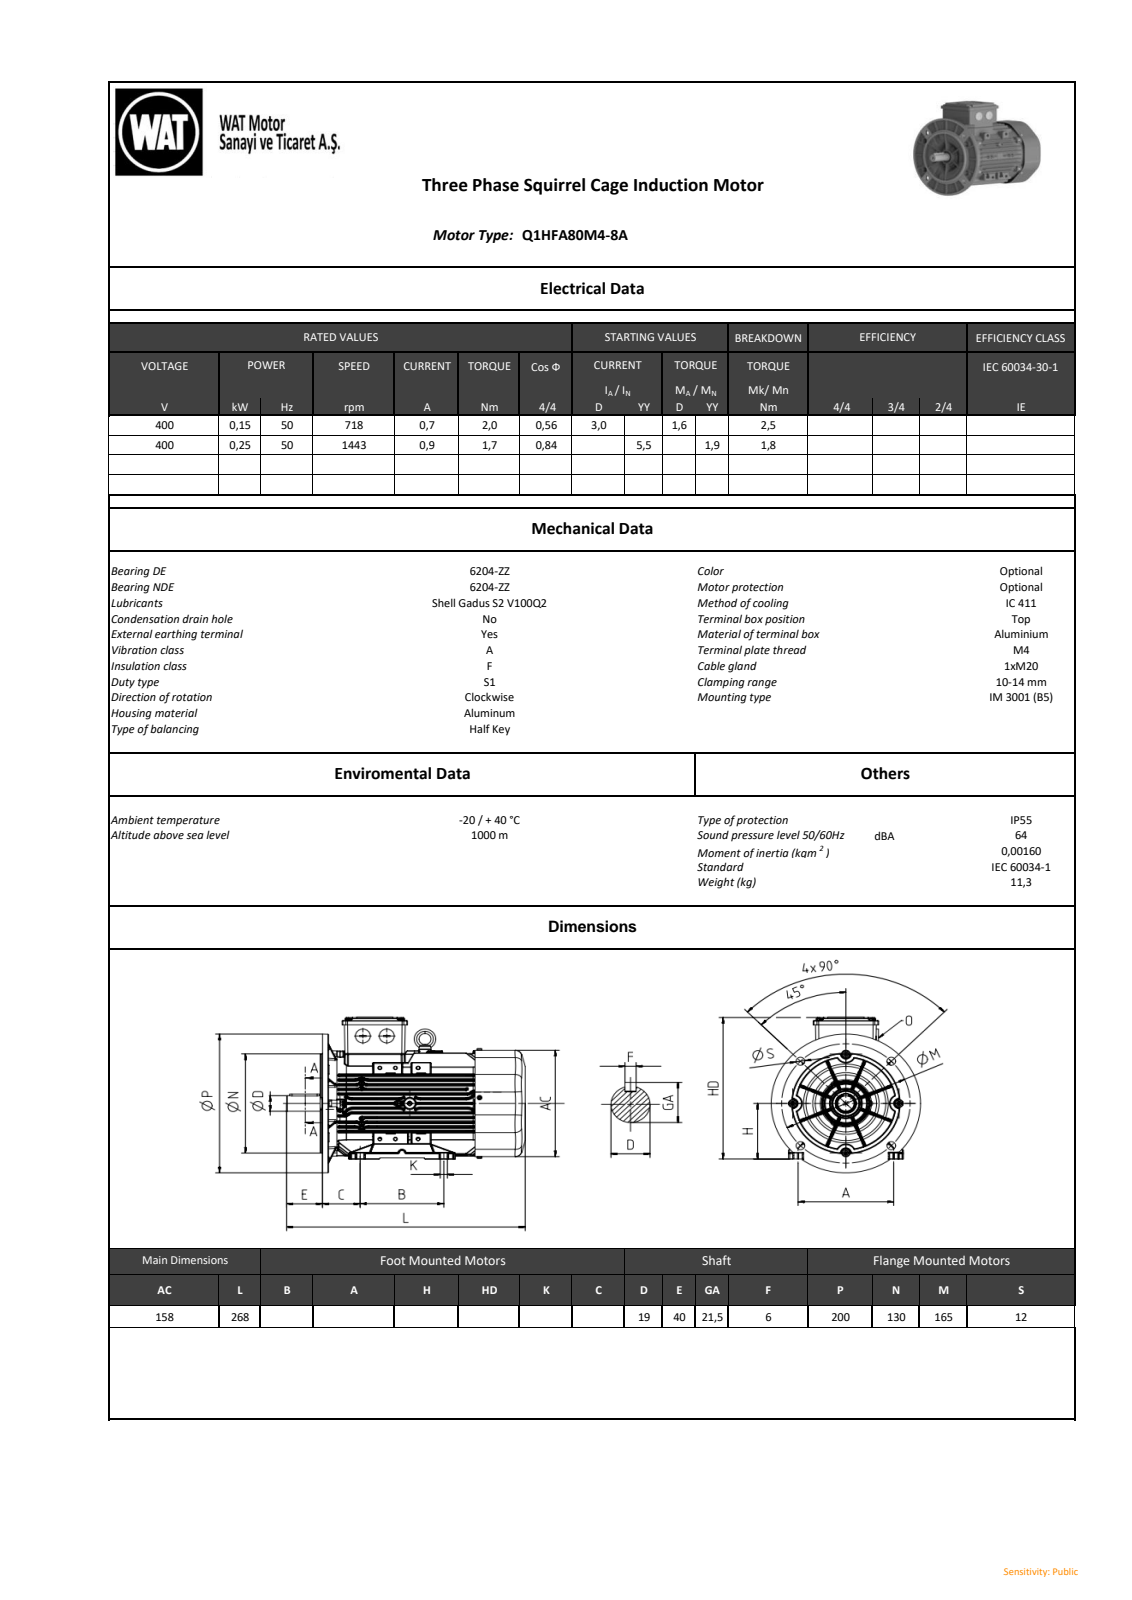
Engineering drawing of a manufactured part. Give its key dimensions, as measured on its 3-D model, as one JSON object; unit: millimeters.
{"part_name": "model1_objects", "step_written_by": "SIEMENS PLM Software NX2206.8101 (AP203_CONFIGURATION_CONTROLLED_3D_DESIGN_OF_MECHANICAL_PARTS_AND_ASSEMBLIES_MIM_LF)", "units": "millimeters", "bodies": {"solids": 0, "faces": 5928, "planar": 1103, "cylindrical": 2286, "other": 2539}, "overall_size": [268, 235.5, 200], "round_holes": [[4.6, 2], [5, 1], [8, 1], [57, 1]], "round_bosses_or_shafts": [[6, 8], [21.38, 2], [146.5, 1], [130, 1], [61, 1], [24.07, 1], [20.2, 1], [20, 1]], "partial_cylinders_radius": [[1, 560], [0.5, 554], [0.8, 333], [2, 124], [1.5, 48], [0.5, 16], [5, 14], [1, 12]], "face_to_face_distances": [1, 41.96, 157, 4.1, 156.98, 10.36, 8.05, 3.95, 86, 10.49], "hole_center_spacings": [70.94]}
